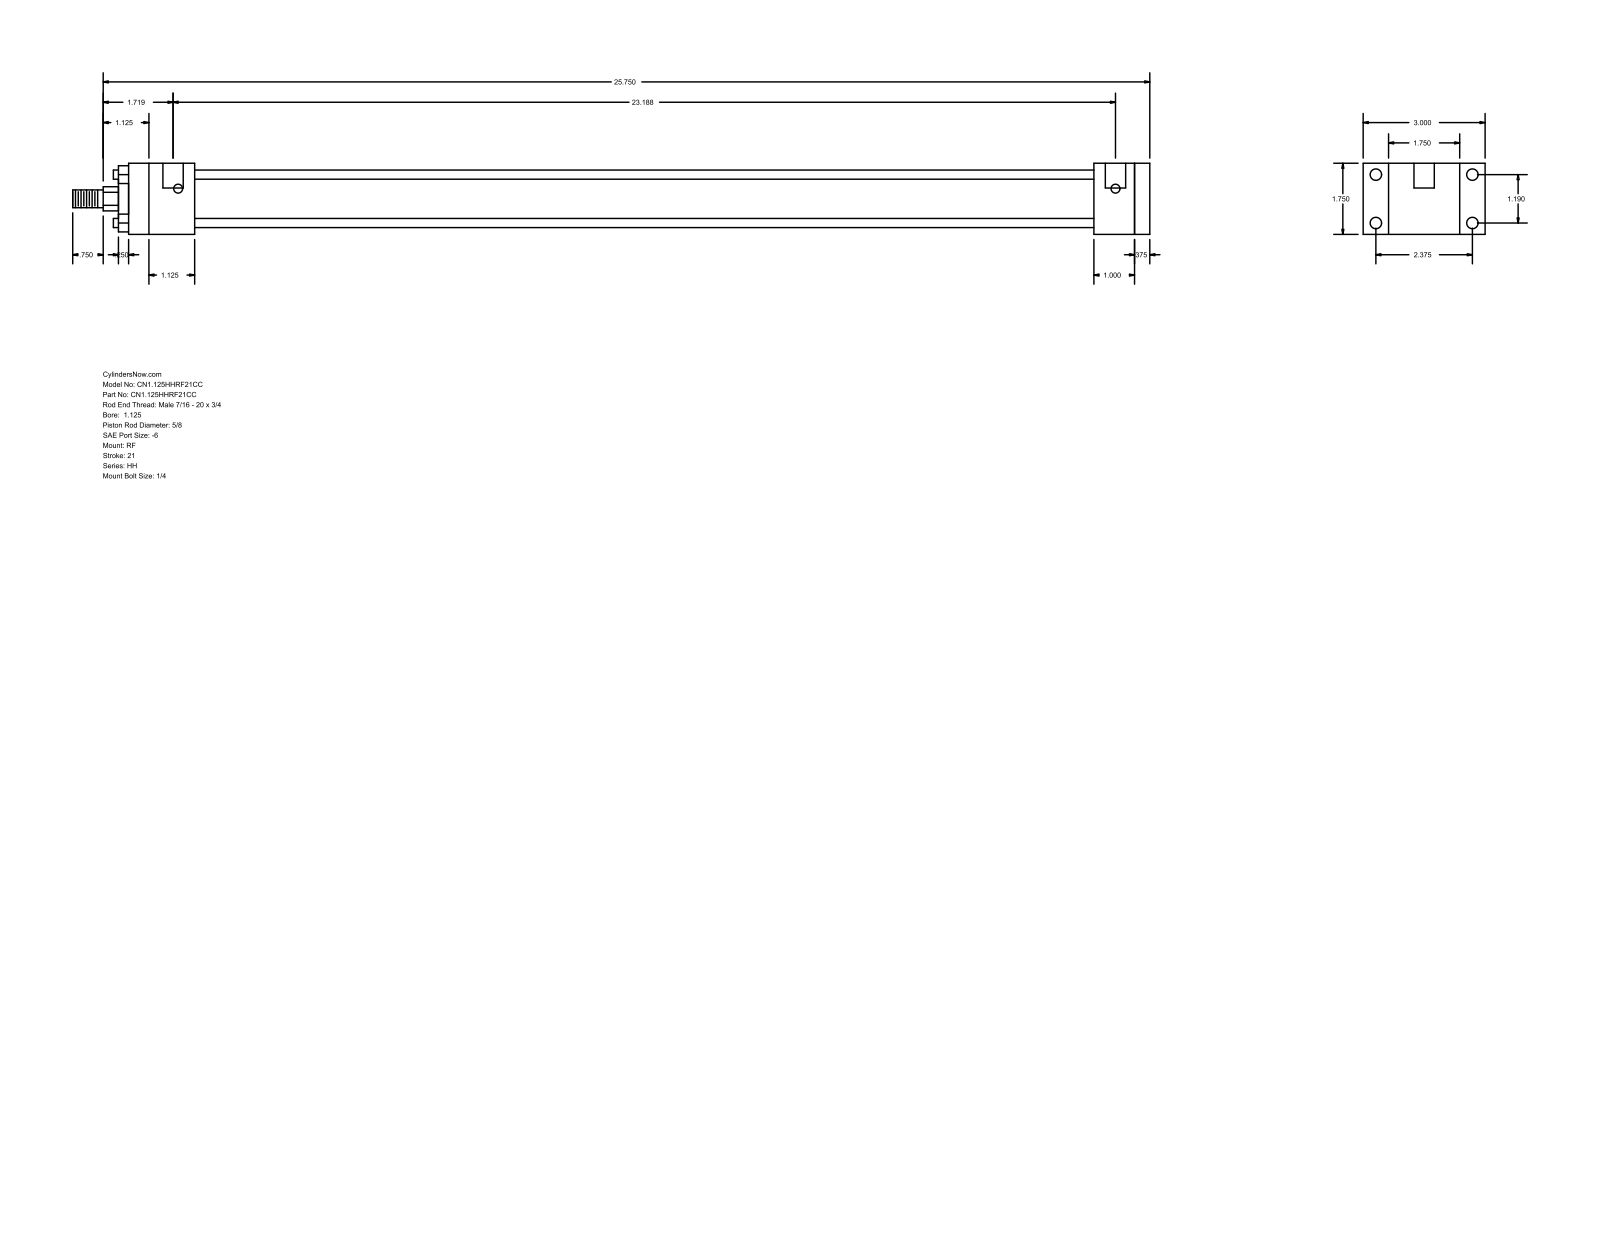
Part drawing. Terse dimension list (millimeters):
name: HH_RF__0112_0.625
written by: GSSL Pune (CONFIG_CONTROL_DESIGN)
unit: mm
bodies: 0 solids, 92 faces (64 planar, 28 cylindrical, 0 other)
size: 673.1 × 76.2 × 44.45
holes: 4× ⌀5.56, 4× ⌀7.14, 2× ⌀12.7
bosses: 4× ⌀5.71, 1× ⌀34.92, 1× ⌀28.57, 1× ⌀15.88, 1× ⌀11.11
rounds: 1× R7.54
face distances: 44.46, 9.53, 638.17, 25.4, 34.93, 15.87, 587.37, 596.9, 561.97, 41.27
hole spacings: 30.22, 60.32, 67.47, 585.79, 3.17, 588.96
